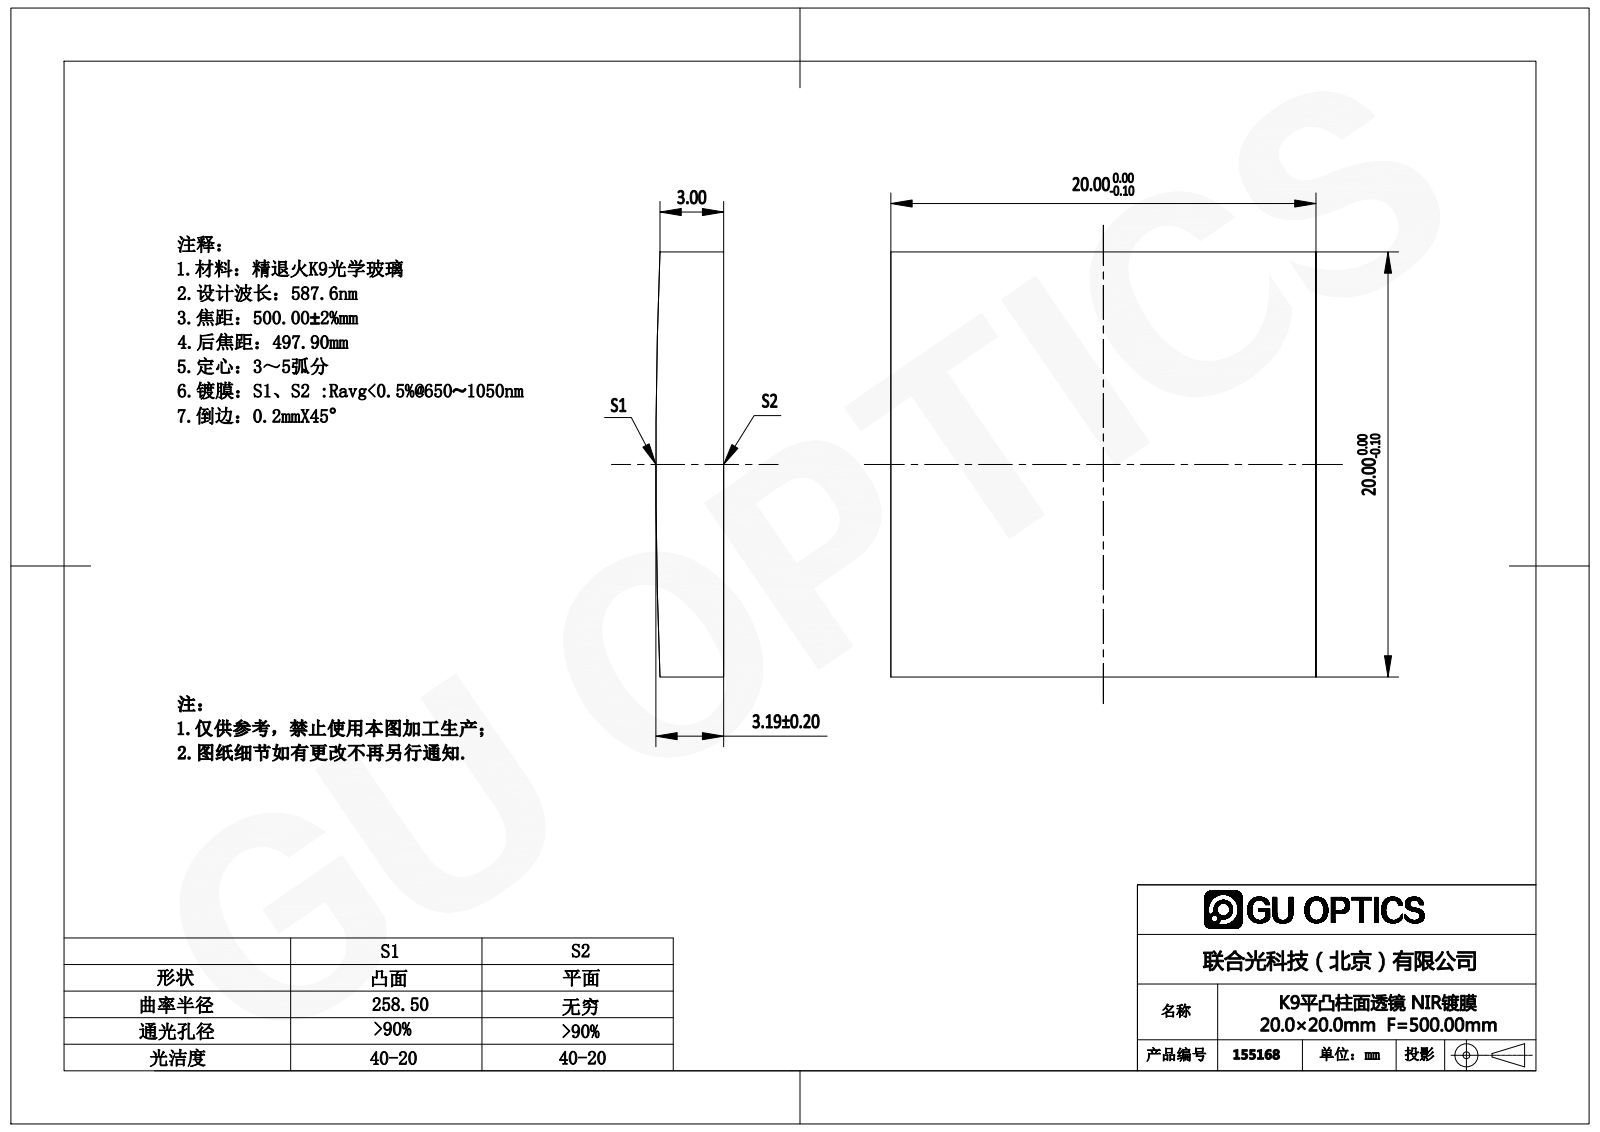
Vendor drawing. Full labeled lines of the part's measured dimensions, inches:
Part name (STEP PRODUCT): 155036
STEP written by: SolidWorks 2016 (AUTOMOTIVE_DESIGN)
Units: inches
Bodies: 1 solid, 6 faces (5 planar, 1 cylindrical, 0 other)
Overall size (bounding box): 0.787 × 0.787 × 0.126
Volume: 0.076 in³ · Surface area: 1.62 in²
Partial cylindrical surfaces — rounded edges, fillets, slot ends (radius × count): R10.177 ×1
Main face-to-face distances: 0.787
